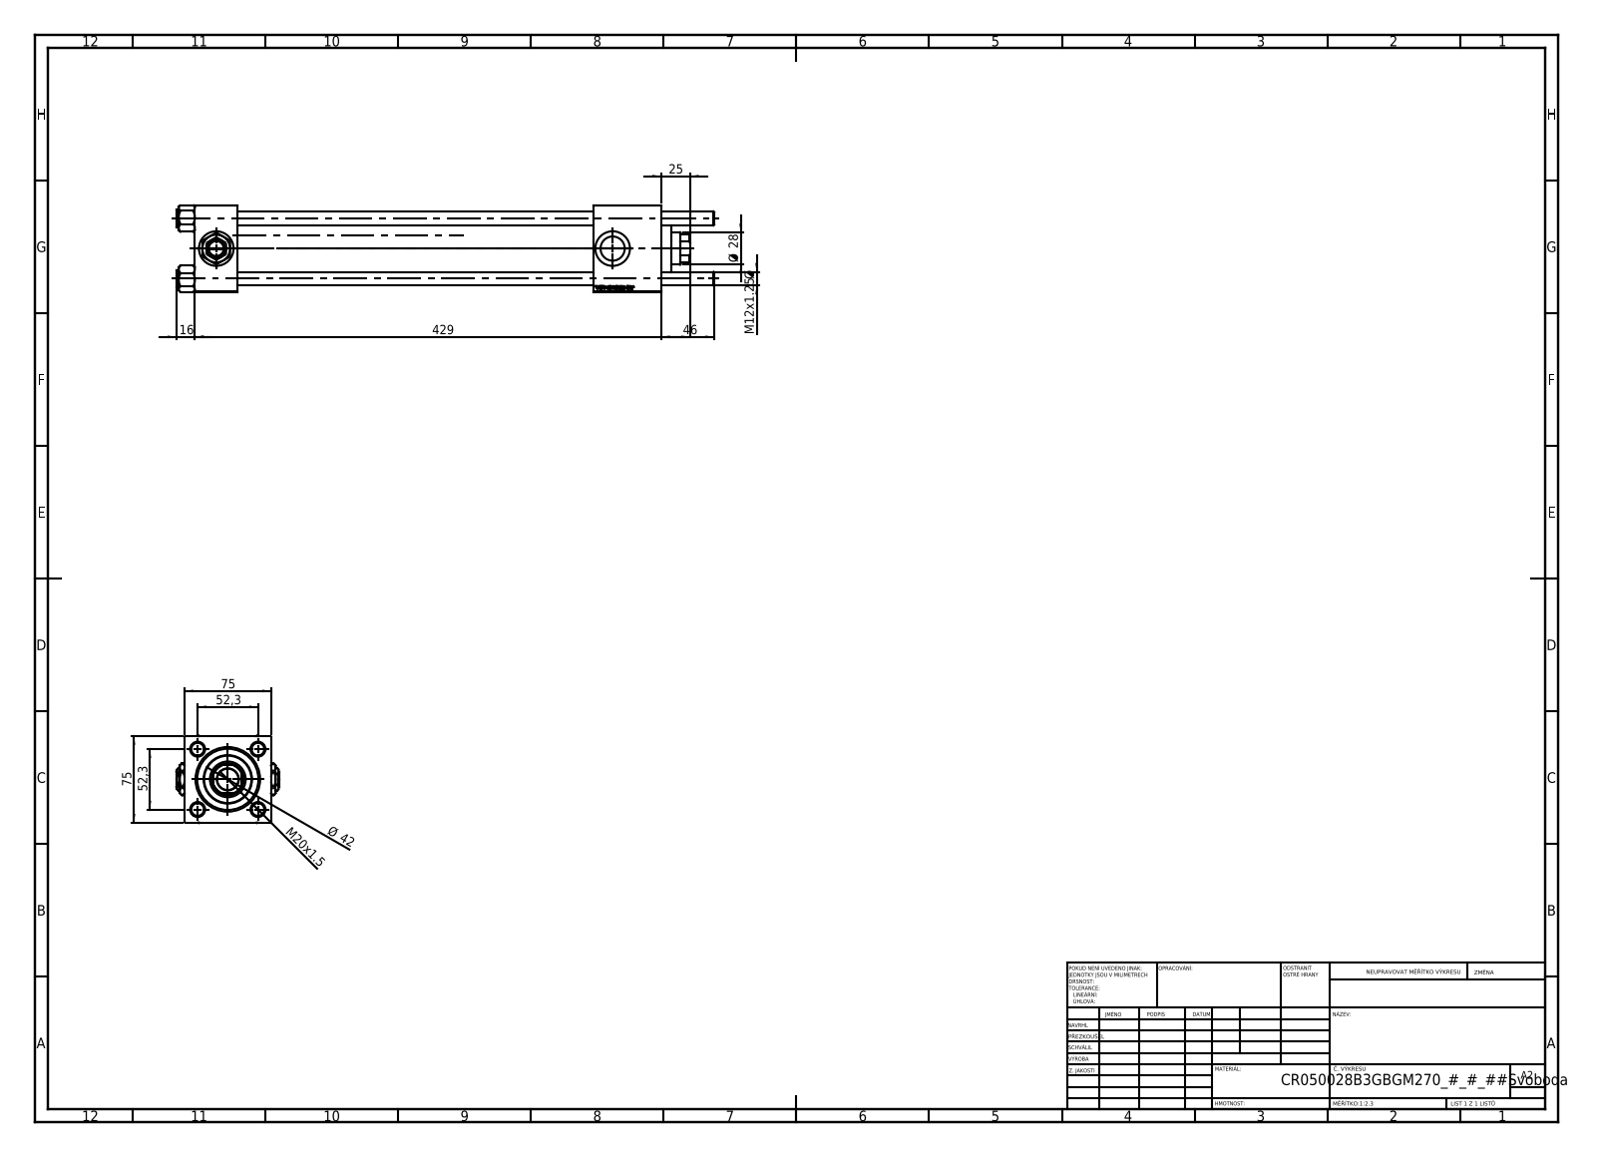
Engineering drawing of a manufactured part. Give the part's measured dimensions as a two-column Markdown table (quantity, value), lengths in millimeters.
| quantity | value |
| --- | --- |
| part name | V215CR_B_TYCINKA; V215_VC_A; Zatka_pro_OIL_PORT; V215CR_VCP_B (+2 more) |
| STEP written by | SolidWorks 2019 (CONFIG_CONTROL_DESIGN) |
| units | millimeters |
| bodies | 13 solids, 1257 faces (479 planar, 88 cylindrical, 690 other) |
| overall size | 466 × 89 × 75.45 |
| volume | 1 089 000 mm³ |
| surface area | 314 556 mm² |
| round holes (diameter × count) | 12 × 4, 7 × 2, 20.96 × 2, 30 × 2, 18.5 × 1, 28 × 1, 31 × 1, 41 × 1, 50 × 1, 53 × 1 |
| round bosses / shafts (diameter × count) | 15 × 4, 56 × 1, 42 × 1 |
| partial cylindrical surfaces (radius × count) | 13.5 × 1 |
| main face-to-face distances | 75, 37, 404, 367, 345, 308, 59, 375.3, 338.3, 30.3 |
| hole center spacings | 36.98, 52.3, 73.96, 343.5 |
